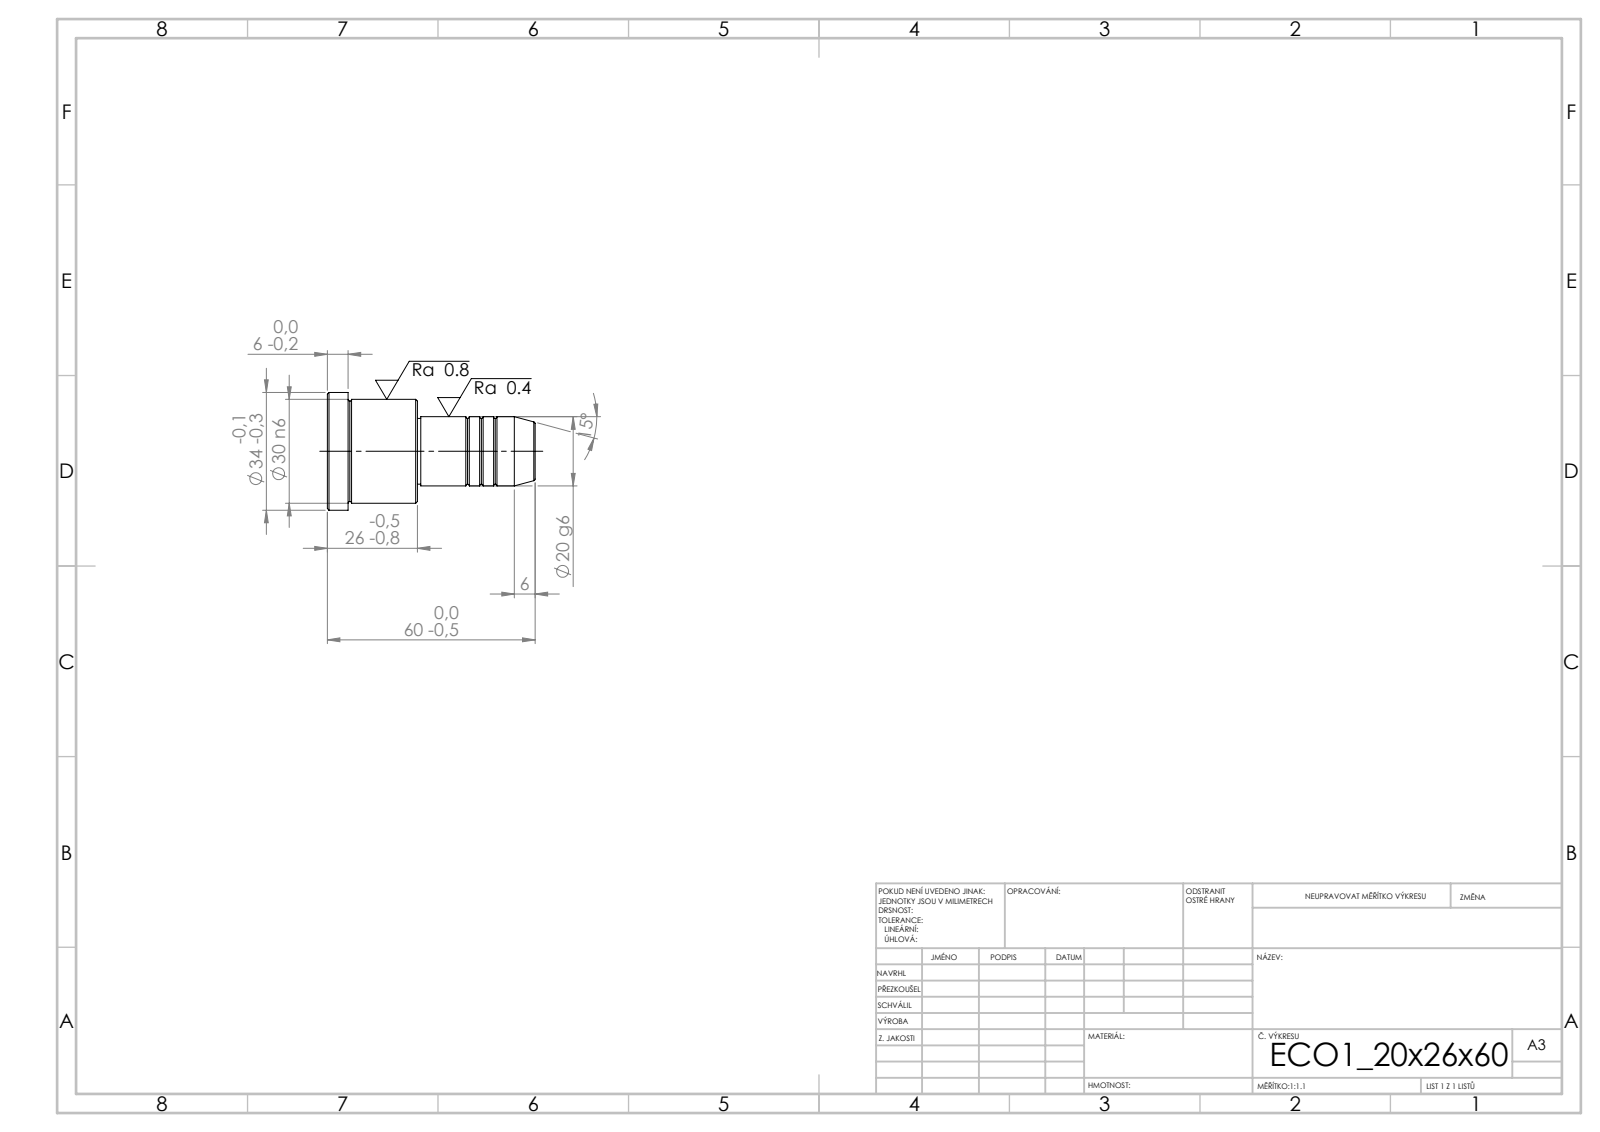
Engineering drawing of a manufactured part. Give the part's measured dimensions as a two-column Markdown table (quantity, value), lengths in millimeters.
| quantity | value |
| --- | --- |
| STEP written by | SolidWorks 2019 (CONFIG_CONTROL_DESIGN) |
| units | millimeters |
| bodies | 1 solid, 43 faces (5 planar, 14 cylindrical, 24 other) |
| overall size | 60 × 34 × 34 |
| volume | 29 813 mm³ |
| surface area | 6 508 mm² |
| round bosses / shafts (diameter × count) | 34 × 1, 30 × 1, 20 × 1, 19 × 1 |
| main face-to-face distances | 26, 34, 60, 54, 20, 6, 33, 1, 21, 27 |
